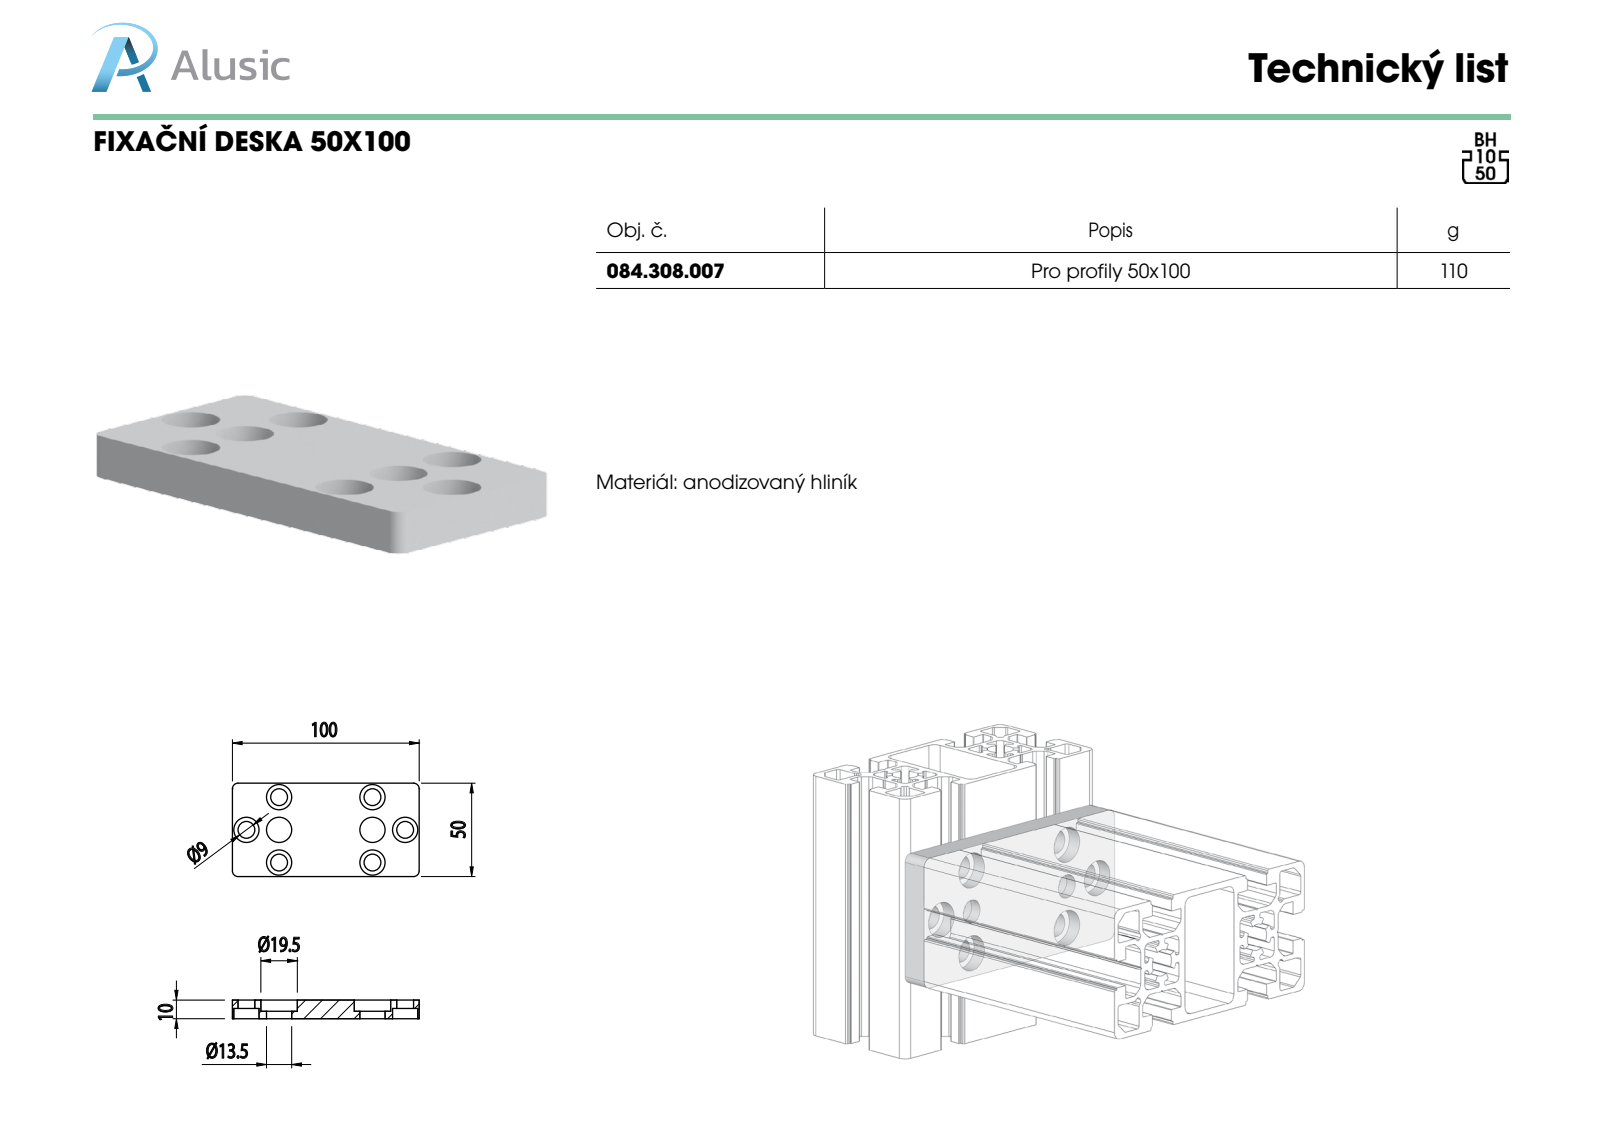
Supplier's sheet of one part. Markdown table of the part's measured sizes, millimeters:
| quantity | value |
| --- | --- |
| part name | 084.308.007 |
| STEP written by | SolidWorks 2012 (CONFIG_CONTROL_DESIGN) |
| units | millimeters |
| bodies | 1 solid, 50 faces (14 planar, 36 cylindrical, 0 other) |
| overall size | 100 × 50 × 10 |
| volume | 38 753 mm³ |
| surface area | 14 834 mm² |
| round holes (diameter × count) | 13.5 × 8, 9 × 6, 19.5 × 2 |
| partial cylindrical surfaces (radius × count) | 3 × 4 |
| main face-to-face distances | 10, 50, 4.5, 5.5, 100, 6, 1.5, 4 |
| hole center spacings | 17.5, 24.75, 52.97, 69.73, 50, 35, 61.03, 67.5 |
